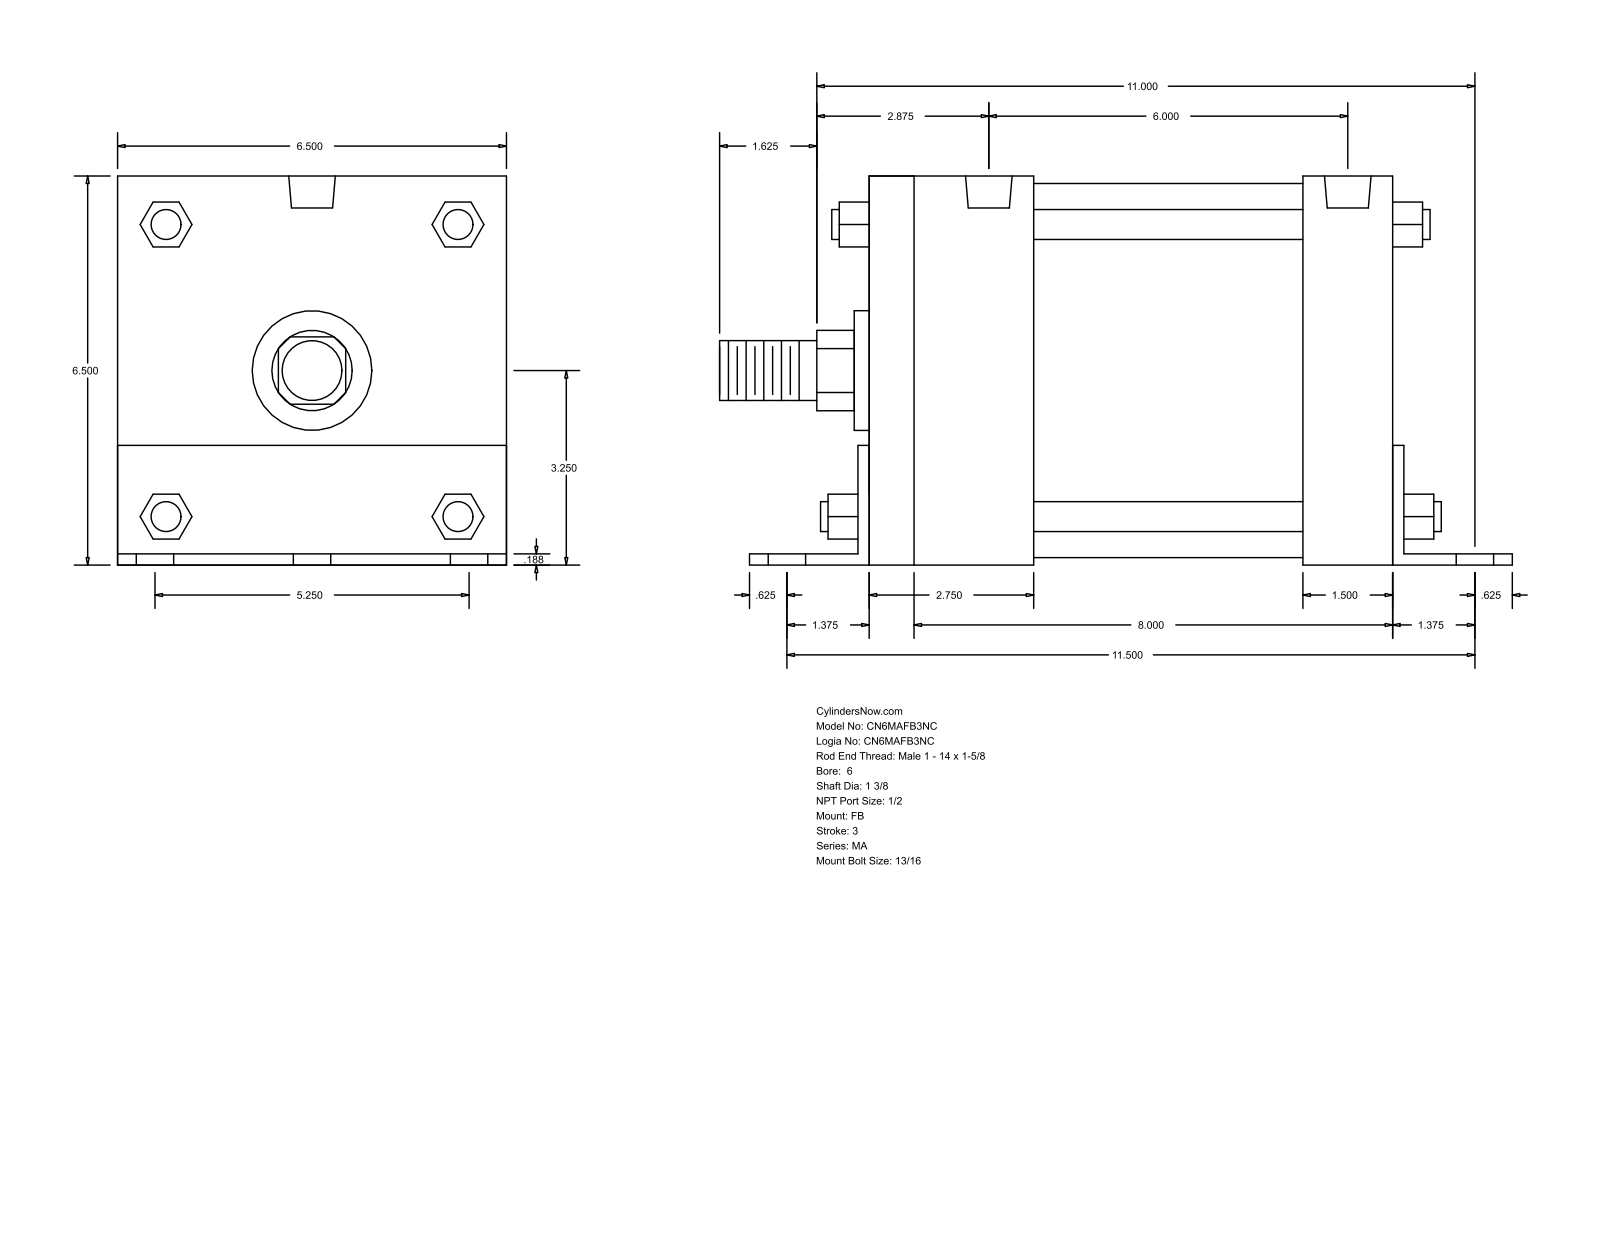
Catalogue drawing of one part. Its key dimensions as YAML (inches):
part_name: "MA_FB__0600_1.375"
step_written_by: "GSSL Pune (CONFIG_CONTROL_DESIGN)"
units: inches
bodies: {solids: 0, faces: 140, planar: 105, cylindrical: 35, other: 0}
overall_size: [13.125, 6.502, 6.5]
round_holes:
  - {diameter: 0.813, count: 6}
  - {diameter: 0.687, count: 4}
  - {diameter: 0.778, count: 2}
round_bosses_or_shafts:
  - {diameter: 0.5, count: 4}
  - {diameter: 6.25, count: 1}
  - {diameter: 2, count: 1}
  - {diameter: 1.375, count: 1}
  - {diameter: 1, count: 1}
partial_cylinders:
  - {radius: 0.672, count: 1}
  - {radius: 1.262, count: 1}
face_to_face_distances: [6.5, 0.187, 8.625, 6.502, 0.185, 6.315, 0.188, 1.5, 1.687, 9]
hole_center_spacings: [2.625, 11.674, 11.375, 3.3, 3.377, 4.276, 5.25, 5.875]
